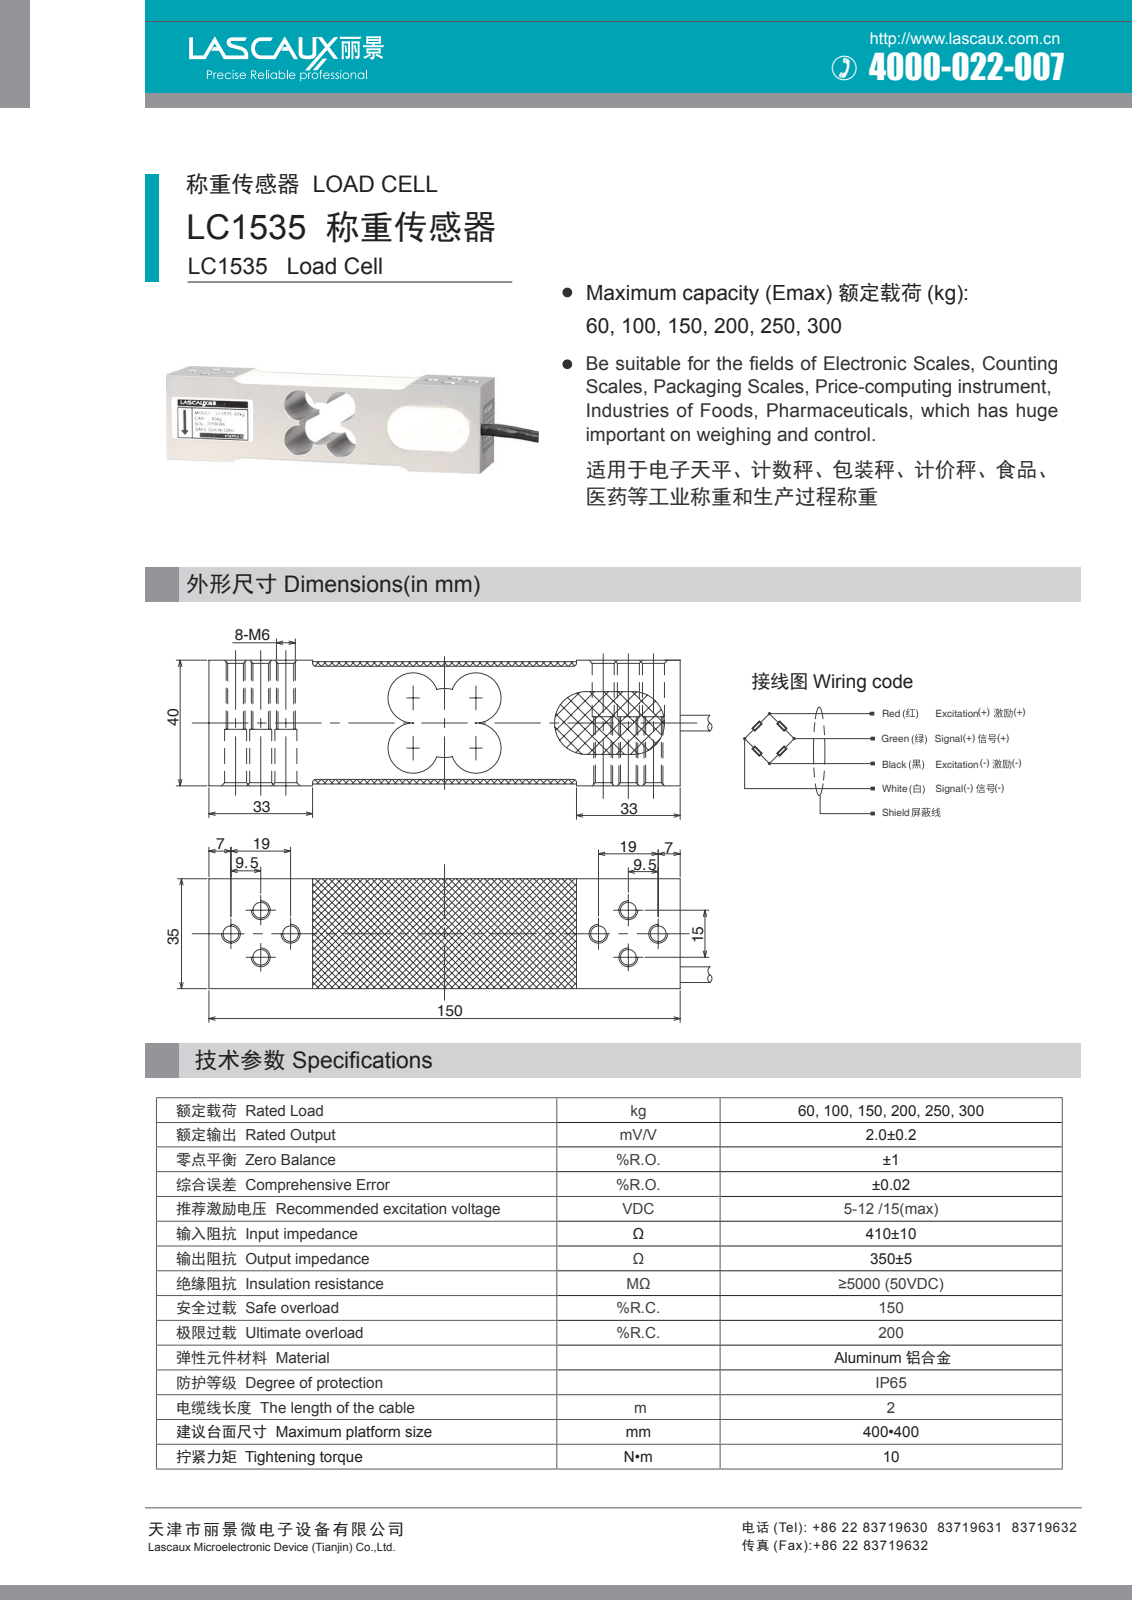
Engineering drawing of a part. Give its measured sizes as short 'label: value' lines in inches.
name: LC1535
written by: SolidWorks 2016 (CONFIG_CONTROL_DESIGN)
unit: in
bodies: 1 solid, 44 faces (18 planar, 26 cylindrical, 0 other)
size: 5.906 × 1.575 × 1.378
volume: 9.446 in³; area: 54.25 in²
holes: 8× ⌀0.276
rounds: 4× R0.039, 4× R0.295
face distances: 1.378, 0.079, 1.496, 1.417, 1.575, 5.906, 0.433, 1.142, 0.354, 1.063
hole spacings: 0.476, 4.243, 4.606, 4.989, 0.591, 0.748, 4.644, 3.858
